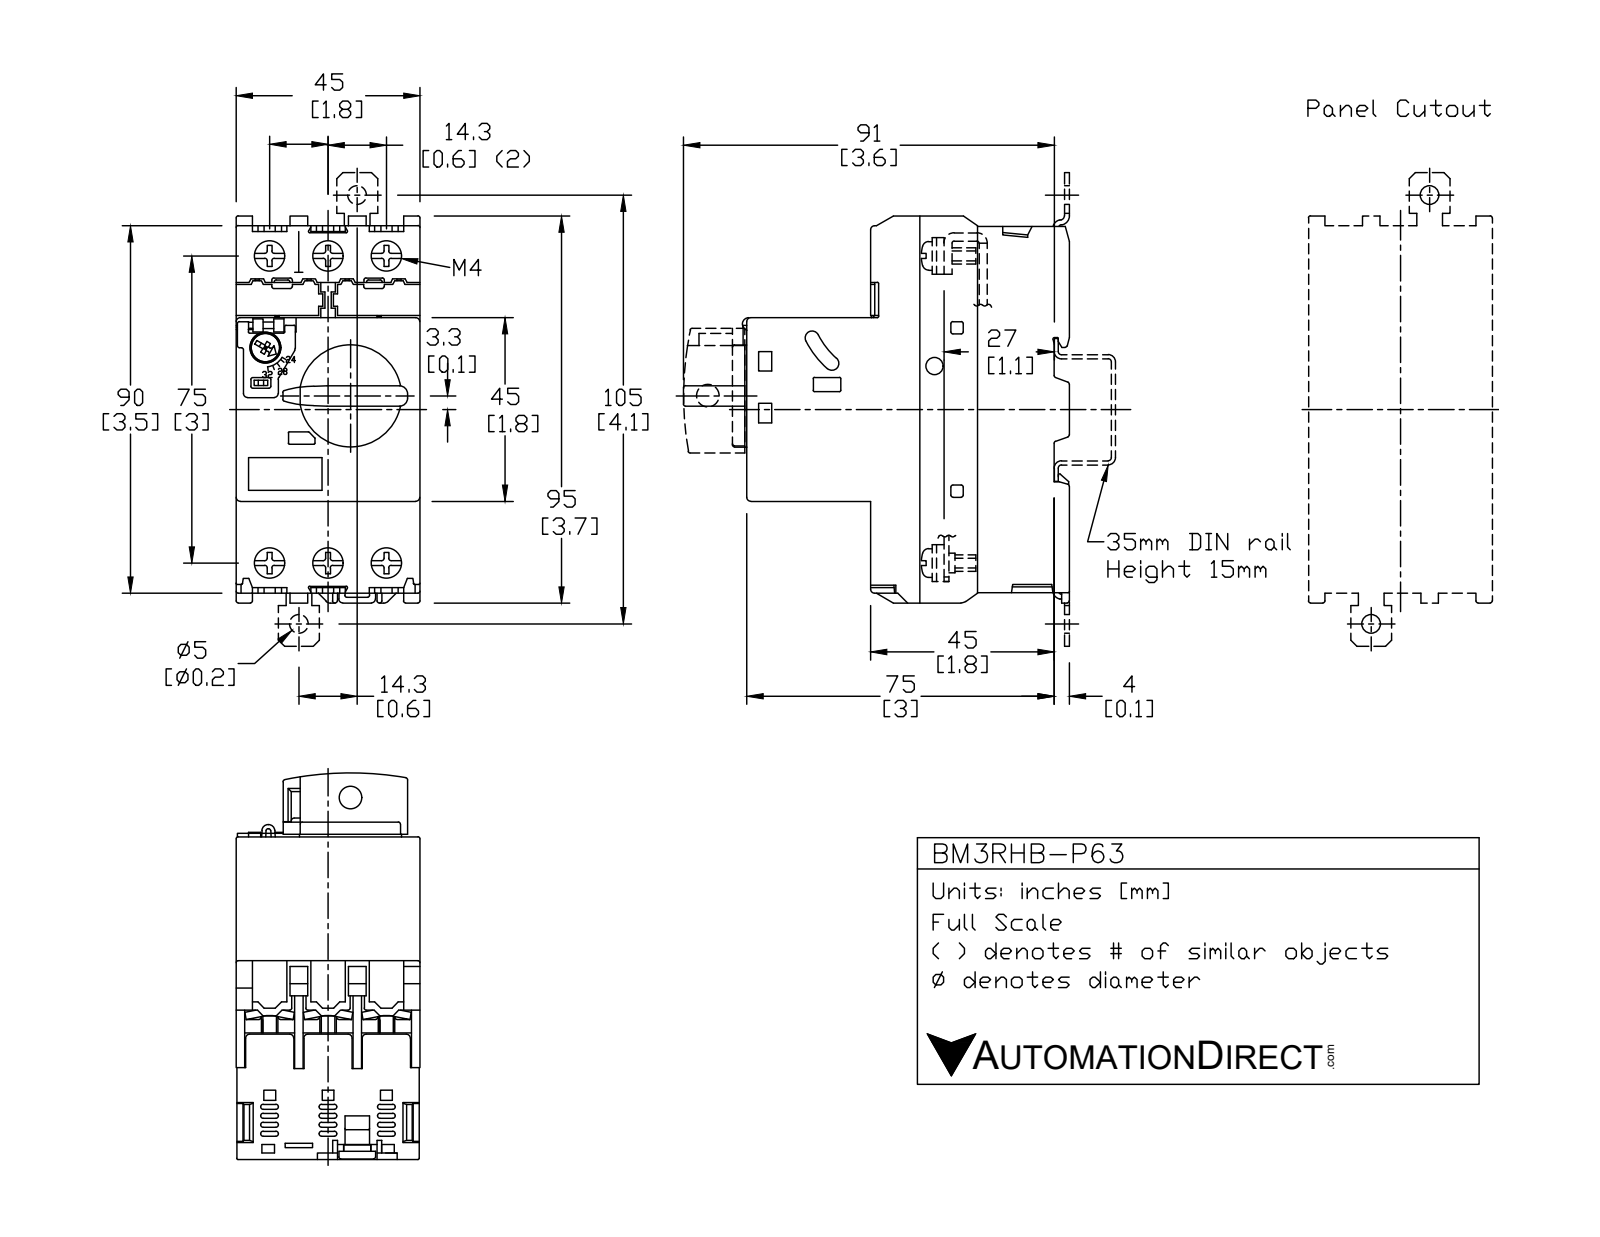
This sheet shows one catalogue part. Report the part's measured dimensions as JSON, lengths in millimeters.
{"part_name": "BM3RHB-P63", "step_written_by": "SolidWorks 2018 (AUTOMOTIVE_DESIGN)", "units": "millimeters", "bodies": {"solids": 25, "faces": 1294, "planar": 964, "cylindrical": 327, "other": 3}, "overall_size": [94.8, 94.5, 45], "volume_mm3": 231500, "surface_area_mm2": 57040, "round_holes": [[4, 6], [7.4, 6], [1.6, 1], [4.2, 1], [5, 1], [5.5, 1], [7.5, 1]], "round_bosses_or_shafts": [[6, 6], [25, 1], [7, 1]], "partial_cylinders_radius": [[0.5, 67], [0.6, 24], [2, 14], [0.3, 12], [1, 8], [2.5, 8], [0.2, 6], [1.5, 2]], "face_to_face_distances": [45, 36.6, 42.4, 79, 22.4, 67.4, 3, 16.5, 20.1, 12], "hole_center_spacings": [14.3, 76.4, 75, 28.6, 80.3, 22.4, 23.9, 27.1]}
